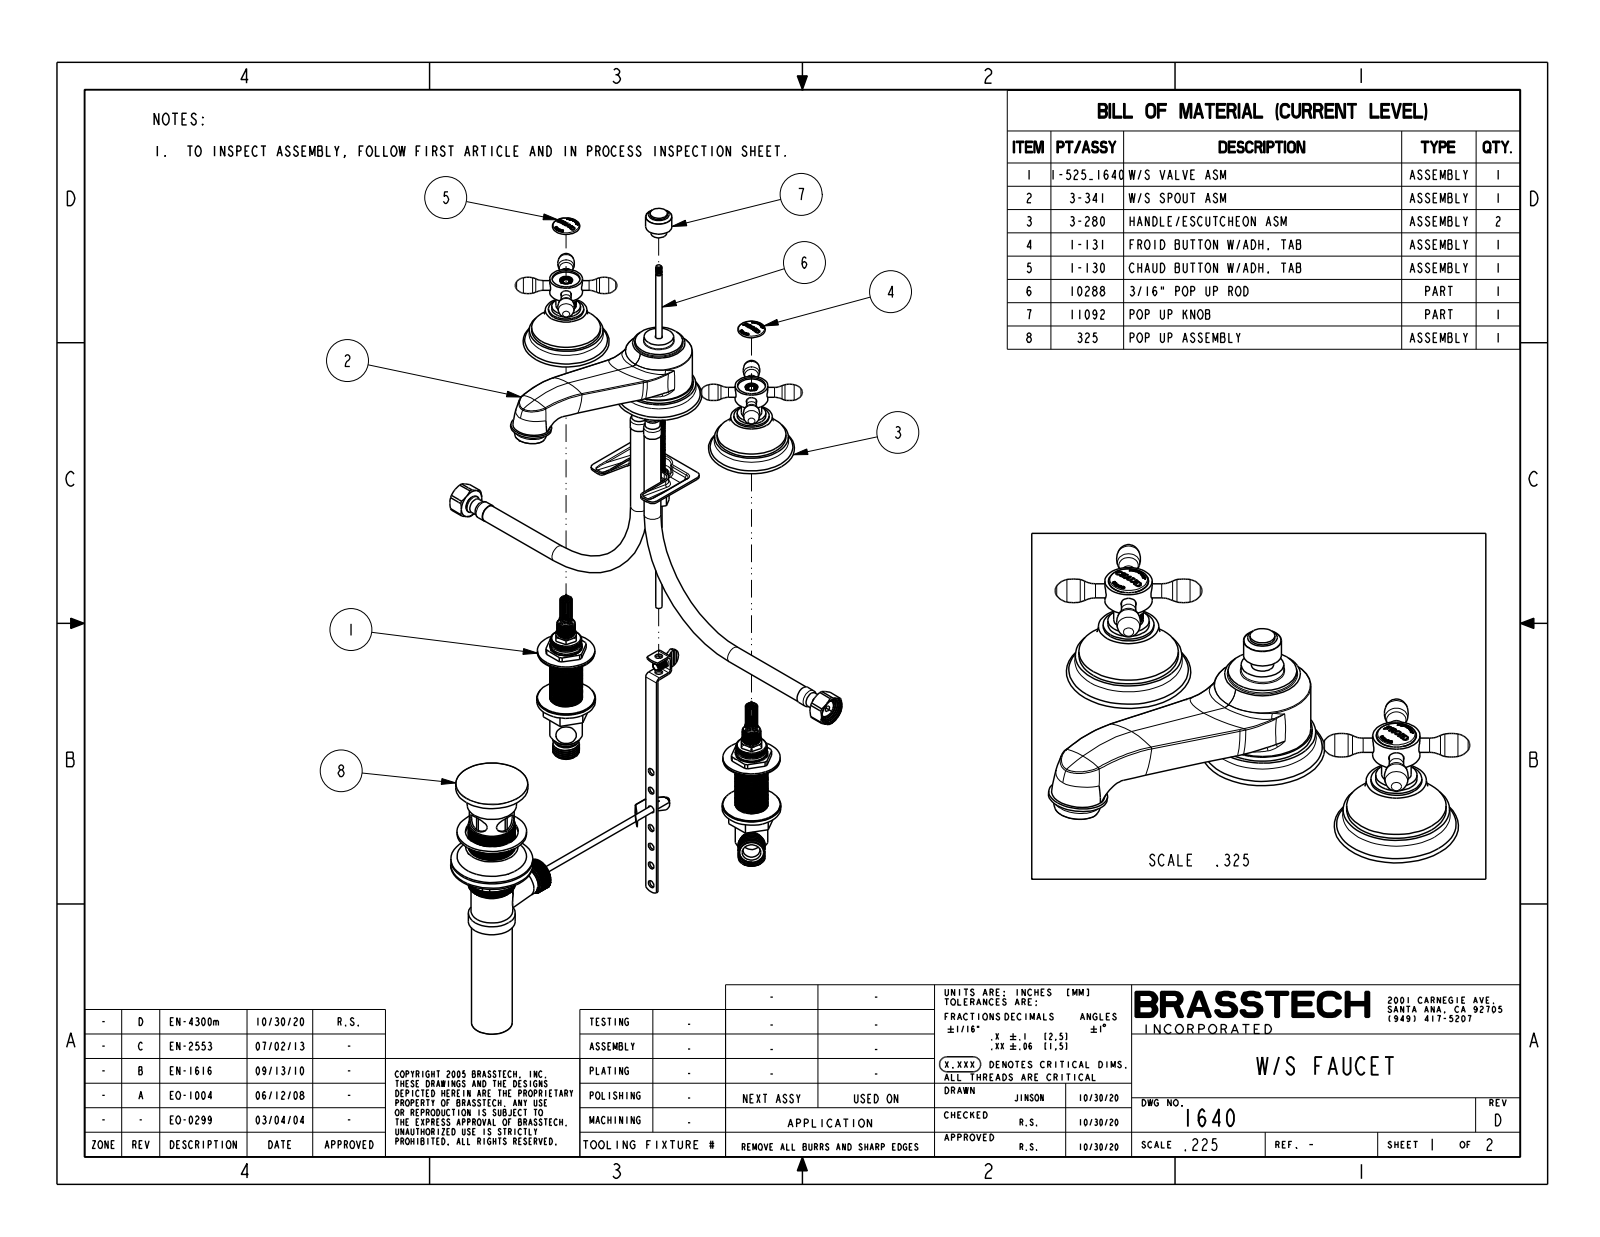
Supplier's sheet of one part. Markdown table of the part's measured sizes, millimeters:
| quantity | value |
| --- | --- |
| part name | 1640 |
| STEP written by | CREO PARAMETRIC BY PTC INC, 2018400 (CONFIG_CONTROL_DESIGN) |
| units | millimeters |
| bodies | 3 solids, 787 faces (303 planar, 225 cylindrical, 259 other) |
| overall size | 269.9 × 189.1 × 75.7 |
| volume | 376 200 mm³ |
| surface area | 62 480 mm² |
| round bosses / shafts (diameter × count) | 7.6 × 8, 53.3 × 3, 25.4 × 3, 27.3 × 2, 22.2 × 2, 15.9 × 2, 10.2 × 2, 52 × 1 |
| partial cylindrical surfaces (radius × count) | 0.3 × 20, 0.1 × 10, 0.2 × 10, 0.6 × 9, 0.2 × 8, 1 × 8, 0.4 × 6, 0.4 × 5 |
| main face-to-face distances | 12.1, 52.6, 40.6, 34.9, 22.9, 17.7, 2.5, 20.3, 31.1, 19.1 |
